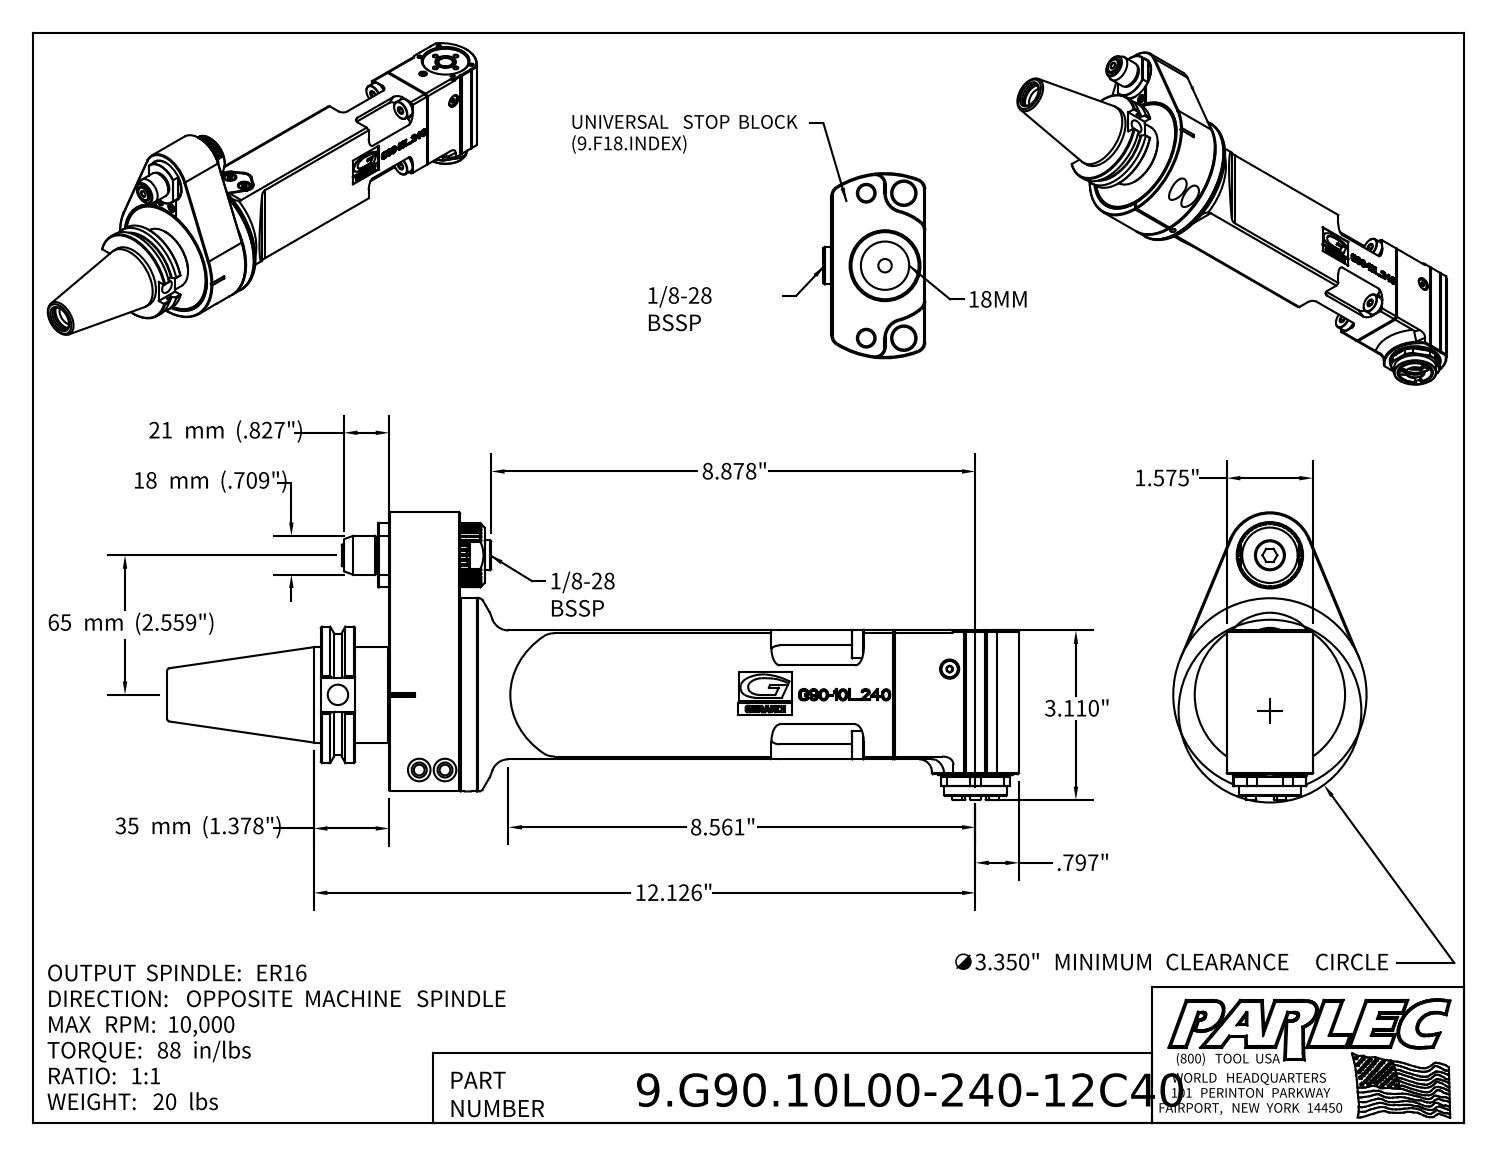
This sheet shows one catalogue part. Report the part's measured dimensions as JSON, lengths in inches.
{"part_name": "9.G90.10L00-240-12C40; 9_GA1_446_1 (Classic, Type 1, Cat40, 65mm); 9_G90_10L240", "step_written_by": "Autodesk Inventor 2022 (AUTOMOTIVE_DESIGN)", "units": "inches", "bodies": {"solids": 4, "faces": 1525, "planar": 950, "cylindrical": 256, "other": 319}, "overall_size": [15.616, 5.276, 3.543], "volume_in3": 45.93, "surface_area_in2": 302.6, "round_holes": [[0.165, 10], [0.335, 5], [0.098, 4], [0.118, 4], [0.197, 4], [0.157, 3], [0.236, 3], [0.413, 3], [0.276, 2], [0.551, 2], [0.709, 2], [1.26, 2]], "round_bosses_or_shafts": [[0.512, 4], [0.669, 2], [0.307, 2], [3.543, 1], [3.228, 1], [3.071, 1], [2.756, 1], [2.5, 1]], "partial_cylinders_radius": [[0.157, 8], [0.236, 4], [0.315, 4], [1.106, 4], [0.079, 3], [0.059, 2], [0.085, 2], [0.197, 2]], "face_to_face_distances": [1.575, 1.299, 2.362, 0.315, 0.197, 0.118, 1.181, 0.984, 0.039, 0.626], "hole_center_spacings": [1.476, 2.557, 0.394, 0.435, 0.557, 0.728, 0.764, 1.087]}
